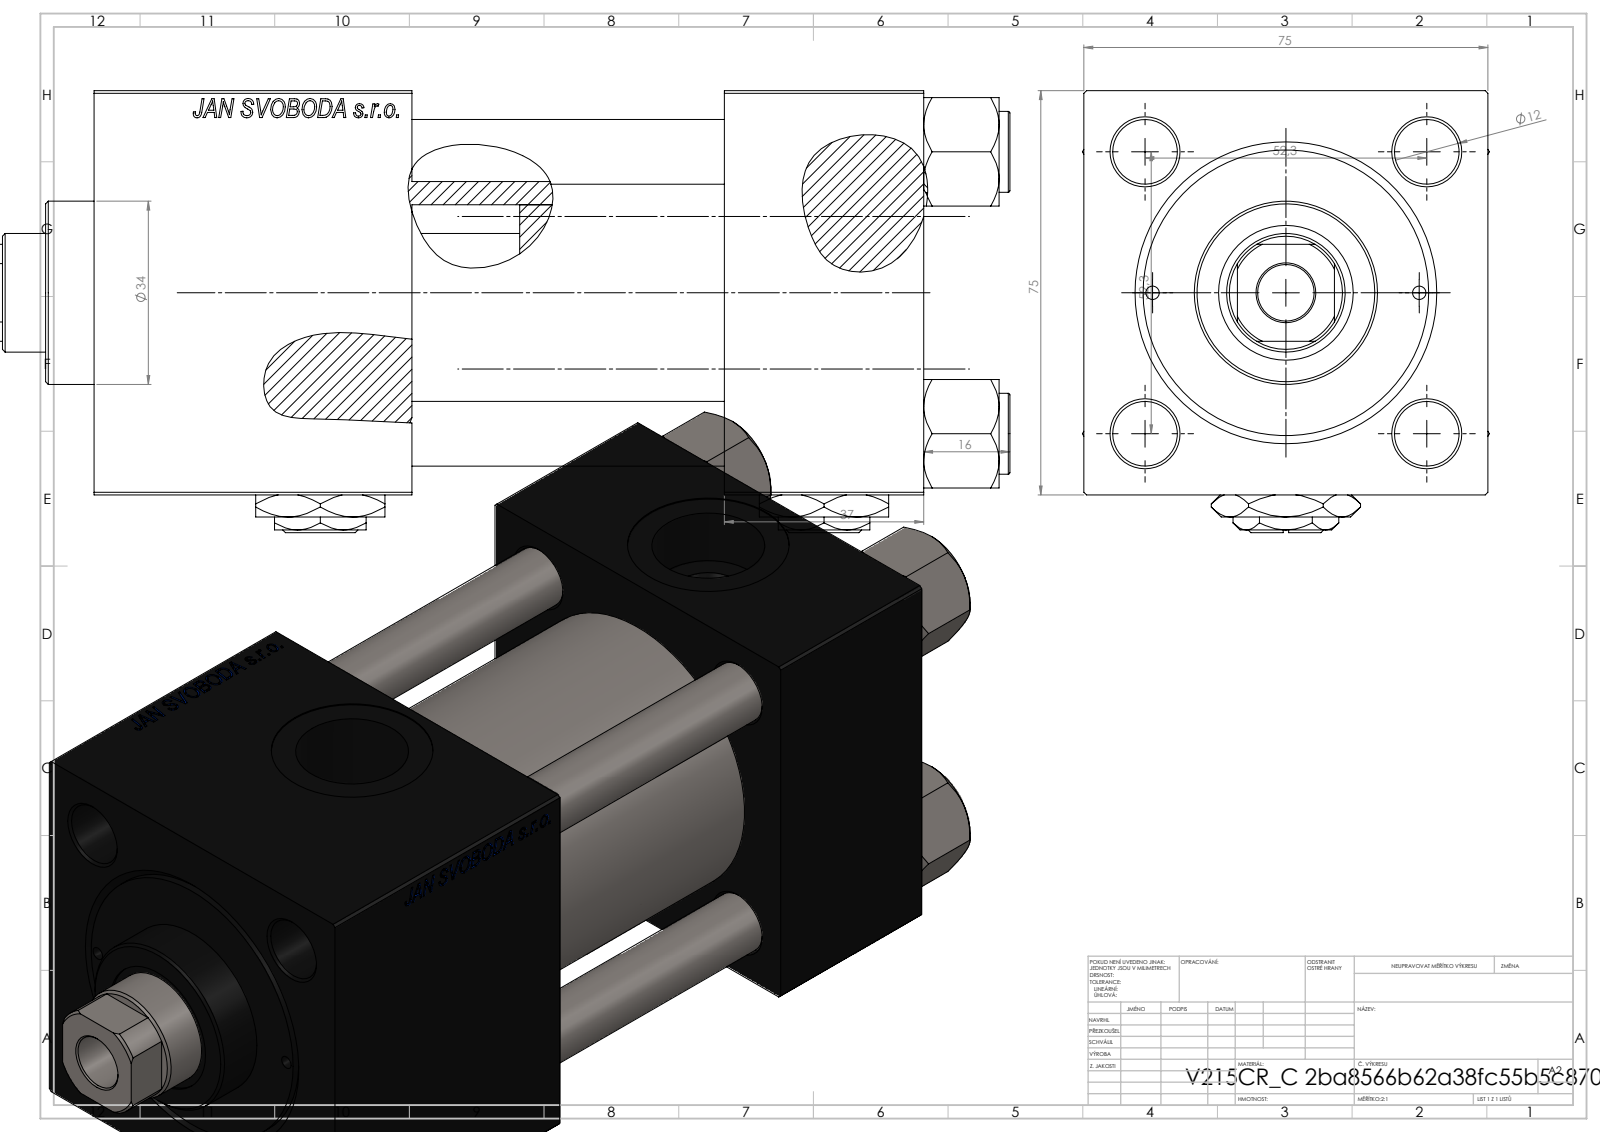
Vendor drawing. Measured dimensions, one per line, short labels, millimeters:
name: V215CR_C_Body; V215CR_VCP_C; V215_VC_A; NUT_M5_C (+2 more)
written by: SolidWorks 2019 (CONFIG_CONTROL_DESIGN)
unit: mm
bodies: 13 solids, 1255 faces (575 planar, 102 cylindrical, 578 other)
size: 195 × 82 × 75.54
volume: 651 202 mm³; area: 151 957 mm²
holes: 4× ⌀12, 2× ⌀2.5, 2× ⌀7, 2× ⌀20.96, 2× ⌀30, 1× ⌀10.5, 1× ⌀22, 1× ⌀25, 1× ⌀41, 1× ⌀50, 1× ⌀53
bosses: 4× ⌀15, 1× ⌀56, 1× ⌀34
rounds: 1× R10.5
face distances: 75, 37, 154, 117, 95, 59, 58, 125.3, 88.3, 30.3
hole spacings: 26.19, 36.98, 52.3, 57.22, 24.75, 73.96, 49.5, 93.5
